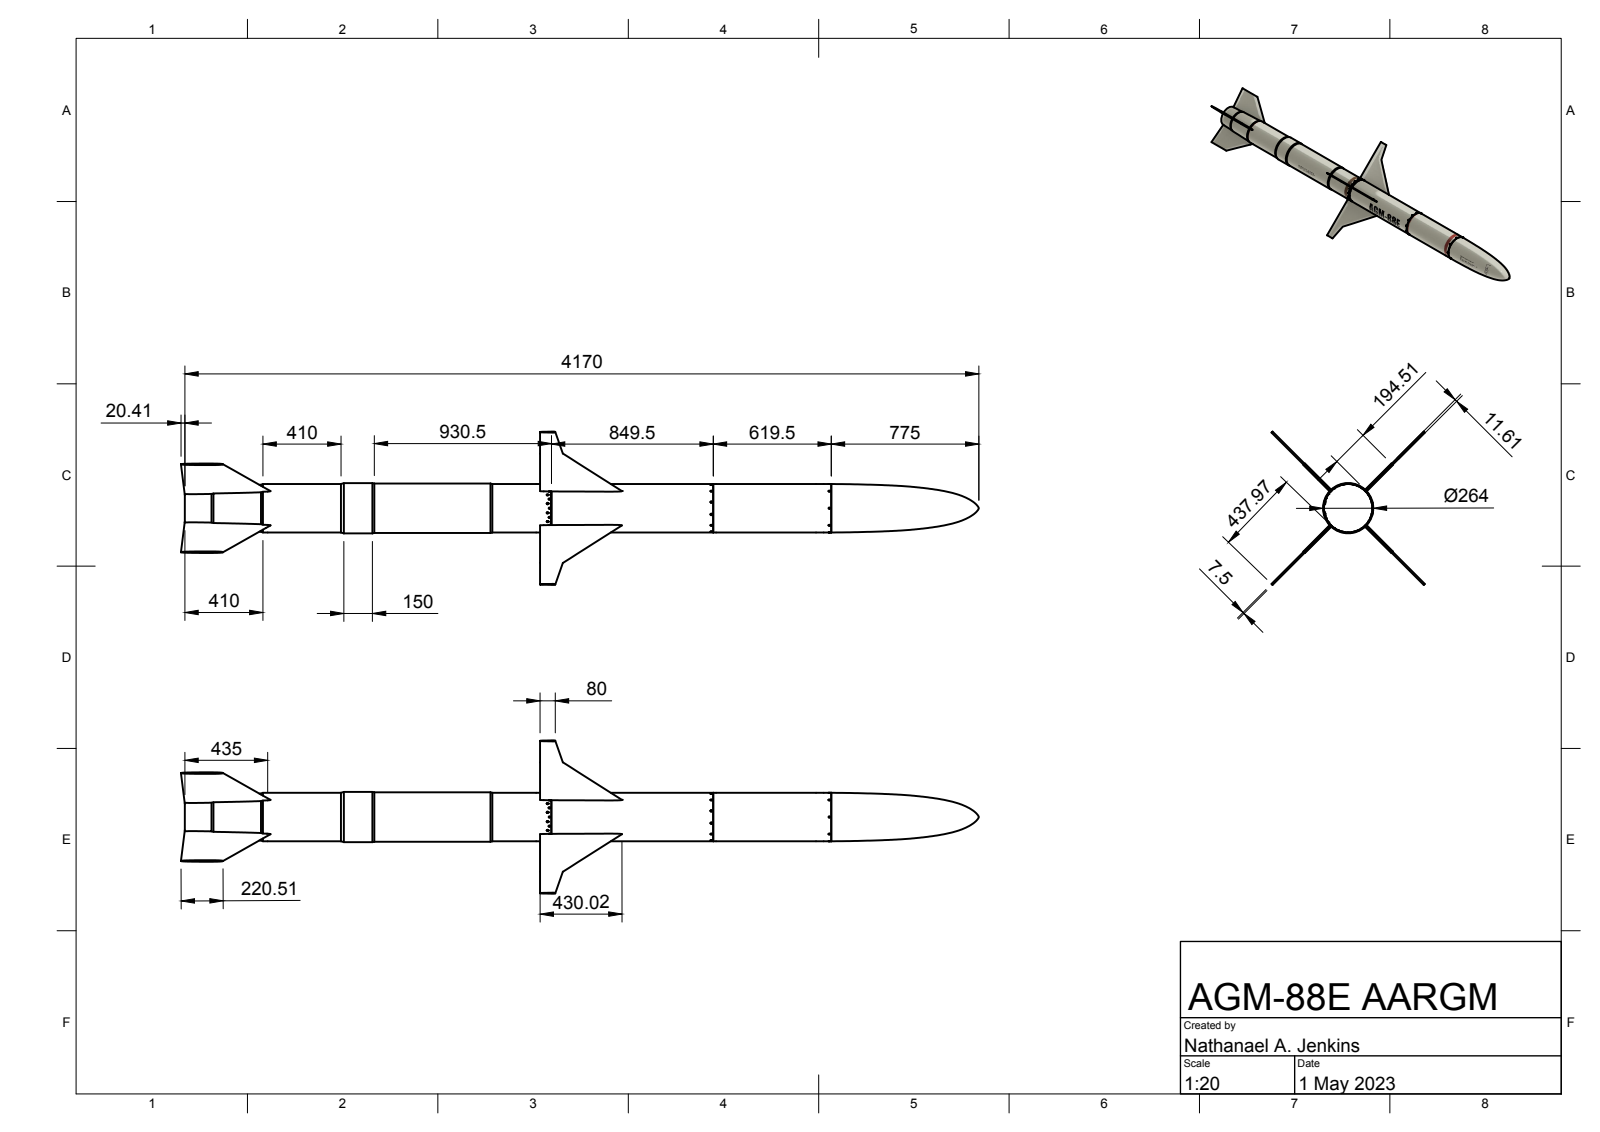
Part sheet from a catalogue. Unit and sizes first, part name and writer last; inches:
Units: inches
Overall size (bounding box): 164.977 × 31.667 × 31.667
Round holes (diameter × count): ⌀7.638 ×1
Round bosses / shafts (diameter × count): ⌀0.315 ×44, ⌀10.394 ×1, ⌀10.197 ×1, ⌀10 ×1
Partial cylindrical surfaces — rounded edges, fillets, slot ends (radius × count): R0.157 ×4
Main face-to-face distances: 0.039, 25.665, 9.408, 35.073, 44.481, 17.237, 27.244, 7.83, 17.836, 10.006
Volume: 12 410 in³ · Surface area: 7 056 in²
Bodies: 1 solid, 222 faces (69 planar, 79 cylindrical, 74 other)
Part name (STEP PRODUCT): AGM-88E AARGM v31; Missile Body
STEP written by: Autodesk Translation Framework v12.4.0.73 (AUTOMOTIVE_DESIGN)
